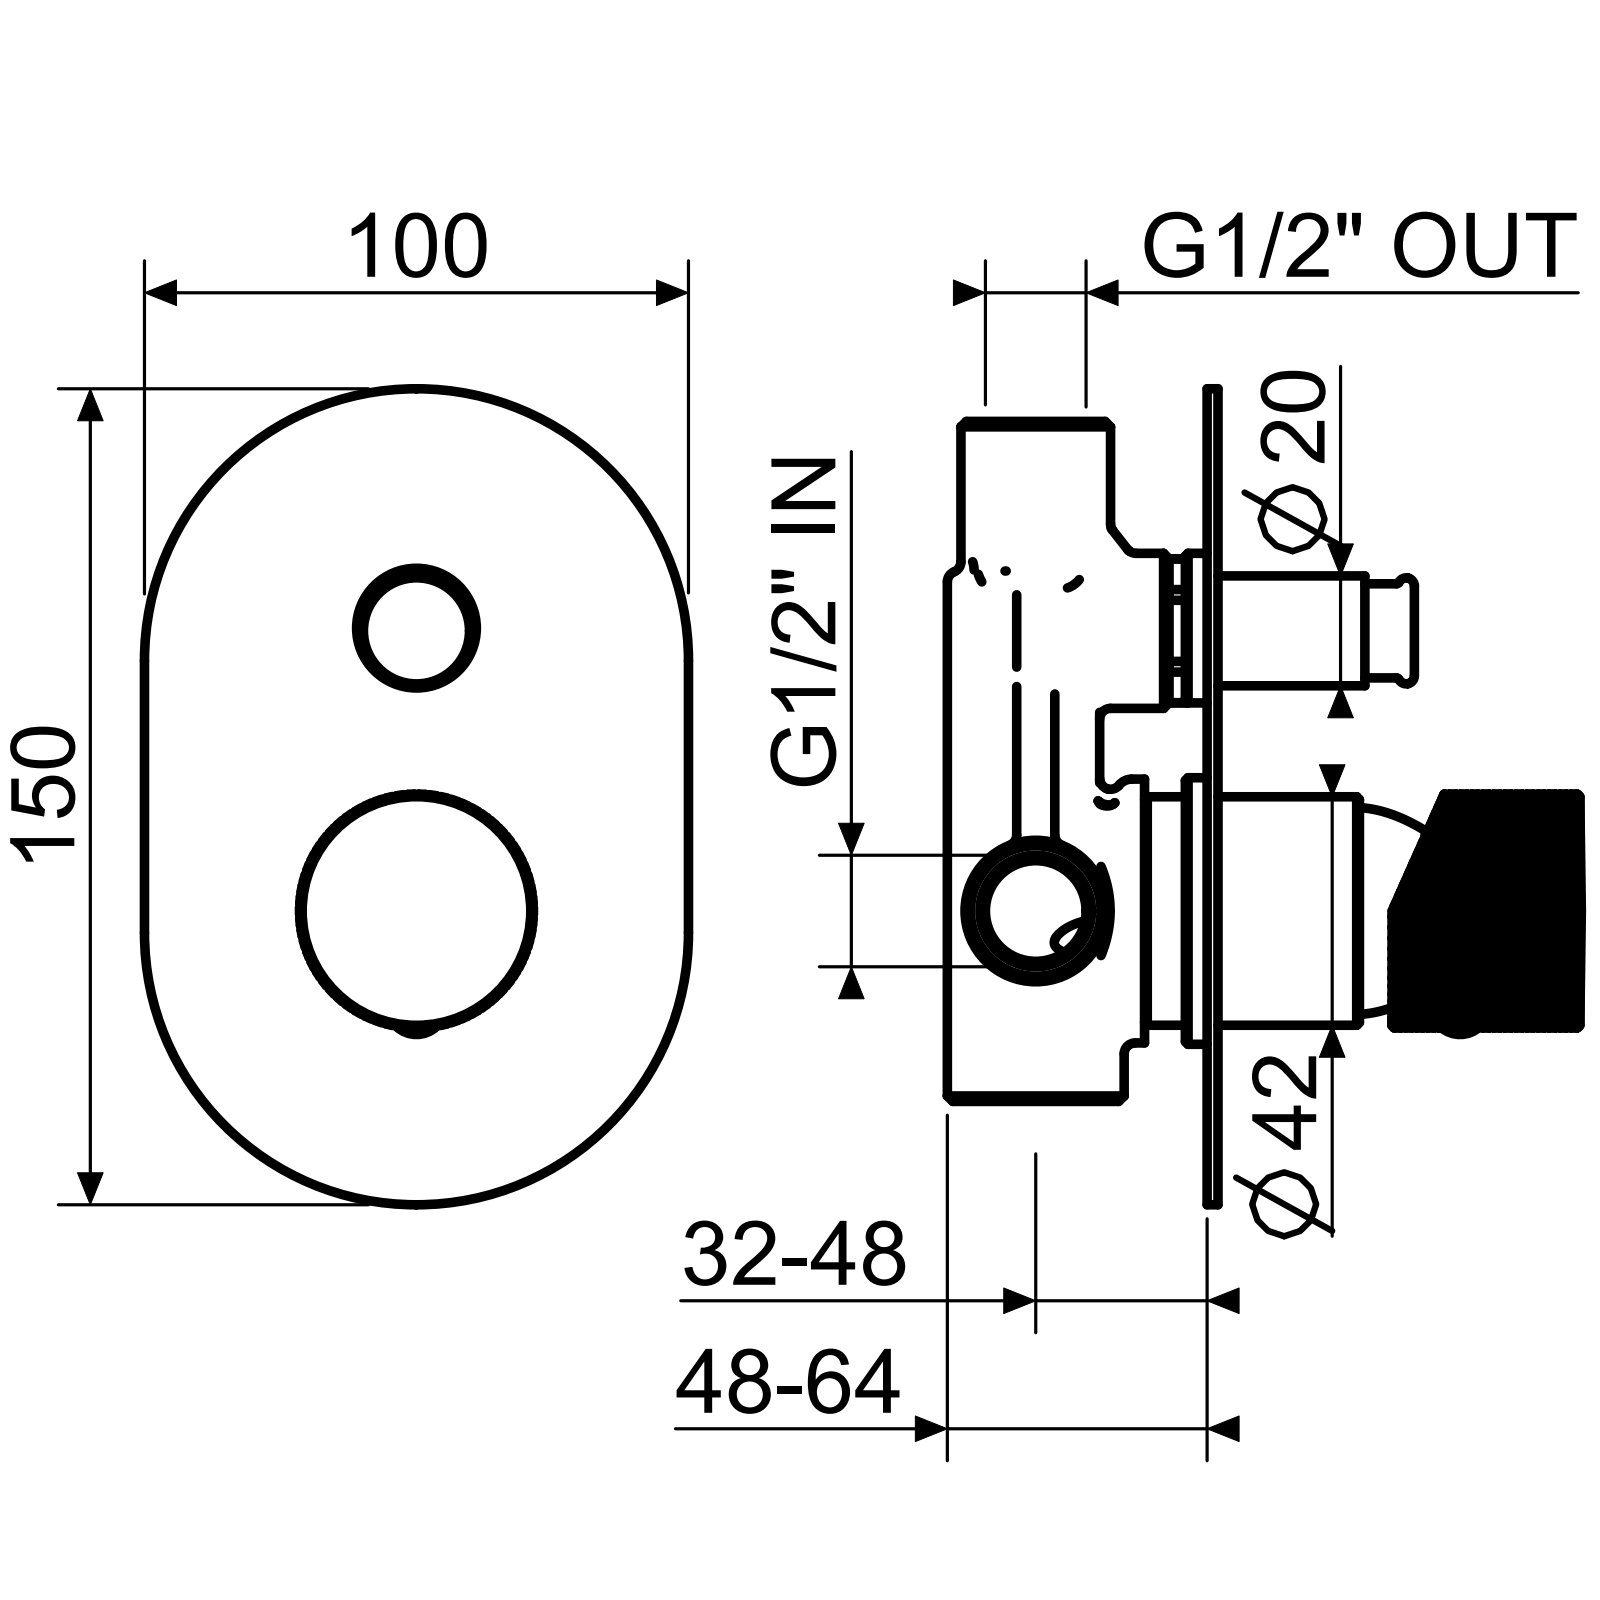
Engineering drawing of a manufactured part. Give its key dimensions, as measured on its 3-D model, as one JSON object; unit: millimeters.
{"part_name": "SINMAC0020; SCCMAC0004; SDVMAC0014; SDVMAC0013 (+8 more)", "step_written_by": "CREO PARAMETRIC BY PTC INC, 2022164 (CONFIG_CONTROL_DESIGN)", "units": "millimeters", "bodies": {"solids": 11, "faces": 5425, "planar": 2126, "cylindrical": 1172, "other": 2127}, "overall_size": [150, 100, 80.29], "volume_mm3": 54890, "surface_area_mm2": 63601, "round_holes": [[2.4, 1], [4.2, 1], [5, 1], [5.1, 1], [6.5, 1], [8, 1], [10.3, 1], [15, 1], [18, 1], [19, 1], [22, 1], [25, 1]], "round_bosses_or_shafts": [[49, 1], [42, 1], [37, 1], [27.5, 1], [20.2, 1], [17.3, 1], [16, 1]], "partial_cylinders_radius": [[0.1, 16], [2.5, 2], [50, 2], [21.5, 1]], "face_to_face_distances": [2, 66, 64, 6, 4, 32, 70, 1, 29.84, 5], "hole_center_spacings": [0.5, 51.5, 52]}
